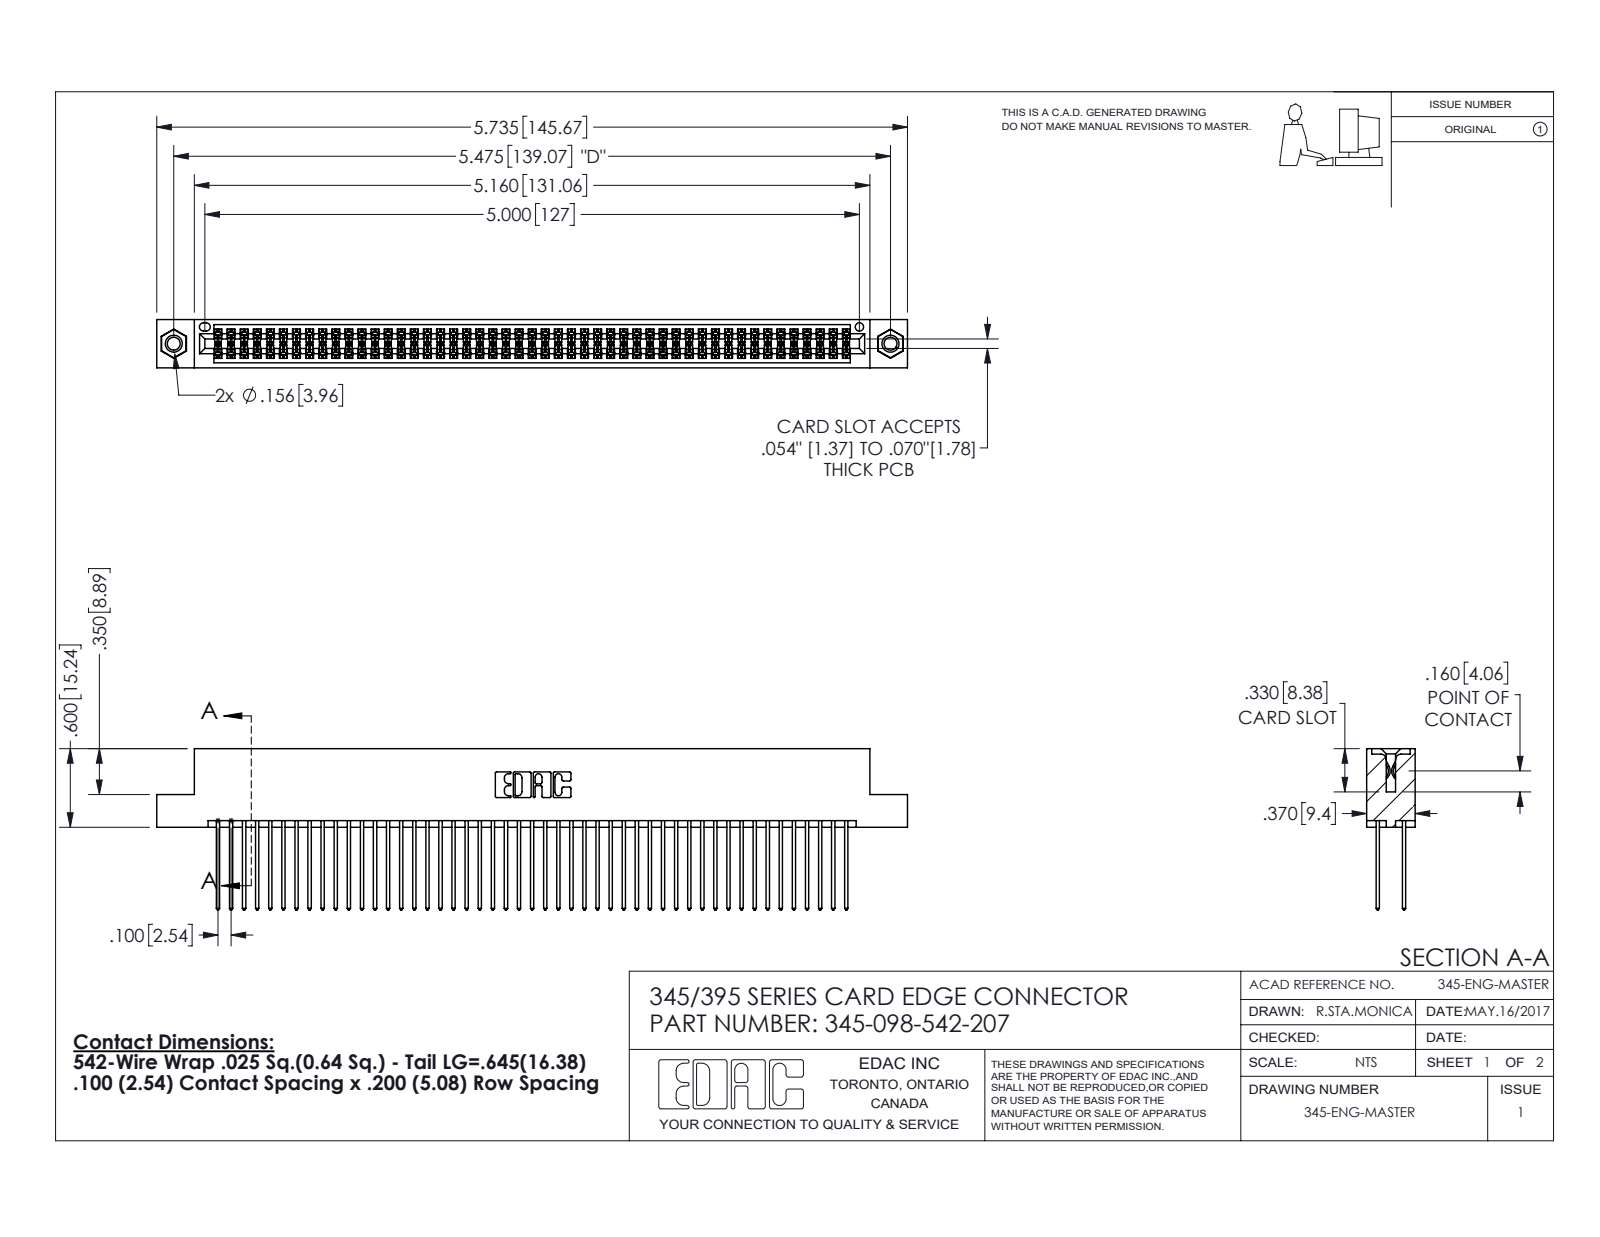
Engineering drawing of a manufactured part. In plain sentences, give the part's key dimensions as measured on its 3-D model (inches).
The part is named "345 Part_Flush Mounting Lugs - 0.156 Dia-TI; 345-292-001_345-293-142; 345-098-542-207; 345-250-001_345-250-005-103". Its 3-D file was written by "SolidWorks 2016 (CONFIG_CONTROL_DESIGN)". It is 101 solids with 5086 faces: 3346 planar, 1724 cylindrical and 16 other. Overall it measures 5.735 by 1.232 by 0.37 inches. Its volume is 0.895 cubic inches and its surface area 37.15 square inches. Round holes: 2 of diameter 0.098, 2 of diameter 0.125, 2 of diameter 0.156, 1 of diameter 0.064. Round bosses or shafts: 2 of diameter 0.155. Partial cylindrical surfaces (rounded edges, fillets, slot ends): 147 of radius 0.006, 98 of radius 0.01, 22 of radius 0.01, 6 of radius 0.007, 6 of radius 0.031, 3 of radius 0.026, 2 of radius 0.014, 2 of radius 0.019. The main face-to-face distances are 0.072, 0.298, 0.2, 0.098, 0.272, 0.025, 0.225, 0.37, 0.175, 0.149. The hole center spacings are 0.27, 5.239, 5.475.
